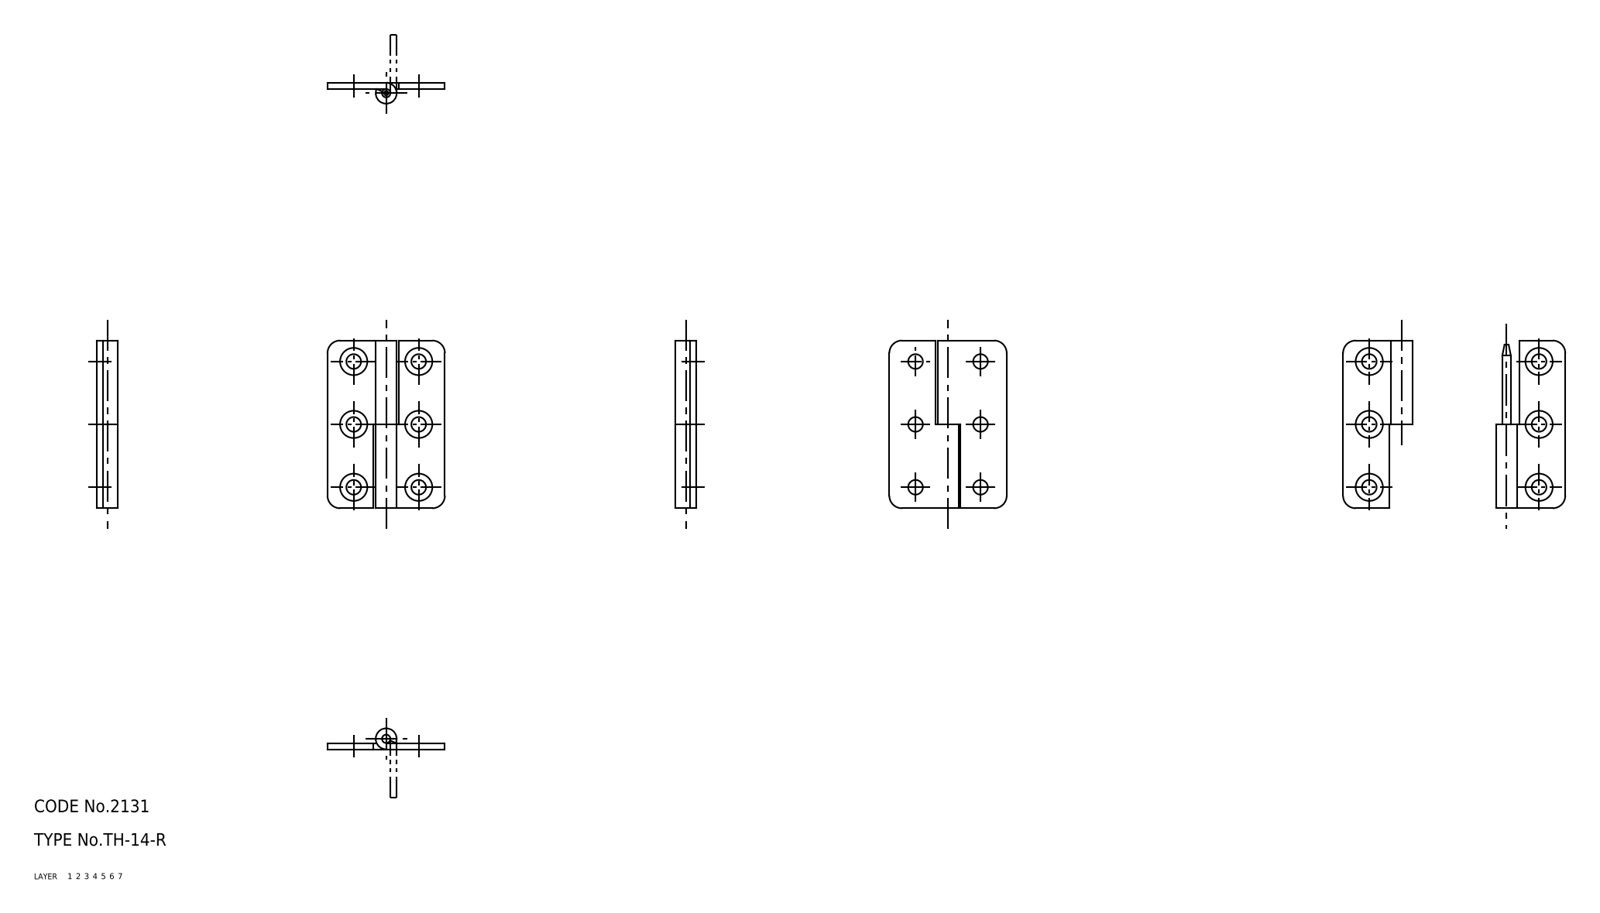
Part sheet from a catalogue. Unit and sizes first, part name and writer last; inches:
Units: inches
Overall size (bounding box): 1.575 × 1.102 × 0.197
Volume: 0.12 in³ · Surface area: 5.034 in²
Bodies: 3 solids, 54 faces (0 planar, 0 cylindrical, 54 other)
Part name (STEP PRODUCT): hinge piece_B_mr; hinge piece_A_mr; shaft; TH_14_R_5659_36
STEP written by: CADfix (AUTOMOTIVE_DESIGN)
